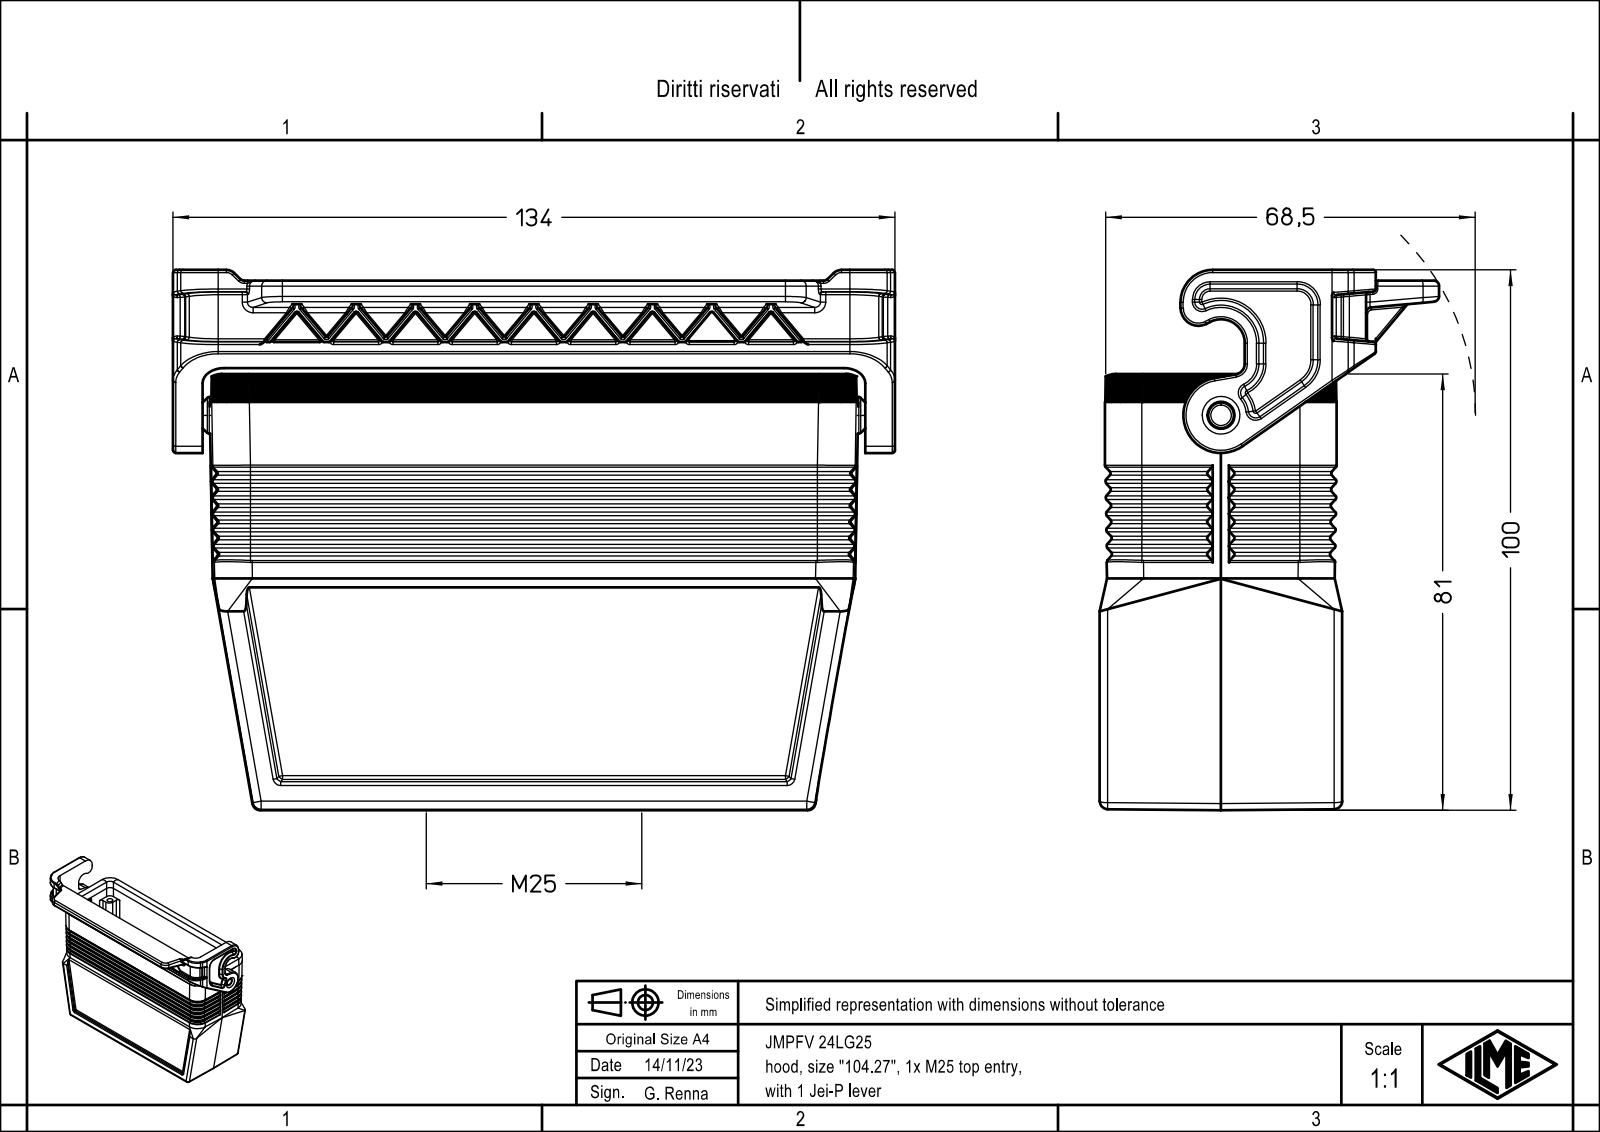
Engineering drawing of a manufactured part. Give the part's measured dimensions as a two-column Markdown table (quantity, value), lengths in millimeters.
| quantity | value |
| --- | --- |
| part name | JMPFV 24LG25 |
| STEP written by | Creo Elements/Direct Modeling 20.1B 02-Apr-2019 (C) Parametric Technology GmbH (AUTOMOTIVE_DESIGN) |
| units | millimeters |
| bodies | 1 solid, 1242 faces (358 planar, 465 cylindrical, 419 other) |
| overall size | 134 × 100.25 × 63 |
| volume | 132 910 mm³ |
| surface area | 70 252 mm² |
| round holes (diameter × count) | 3 × 4, 3.5 × 4, 4.8 × 1, 23.6 × 1 |
| round bosses / shafts (diameter × count) | 6.8 × 1 |
| partial cylindrical surfaces (radius × count) | 0.5 × 147, 0.3 × 126, 1 × 27, 1.5 × 22, 0.33 × 15, 7 × 13, 3 × 12, 4 × 8 |
| main face-to-face distances | 3.75, 39.25, 35.5, 43, 2, 7, 4, 3.25, 42.5, 46.25 |
| hole center spacings | 53.72, 27, 104, 107.45 |
